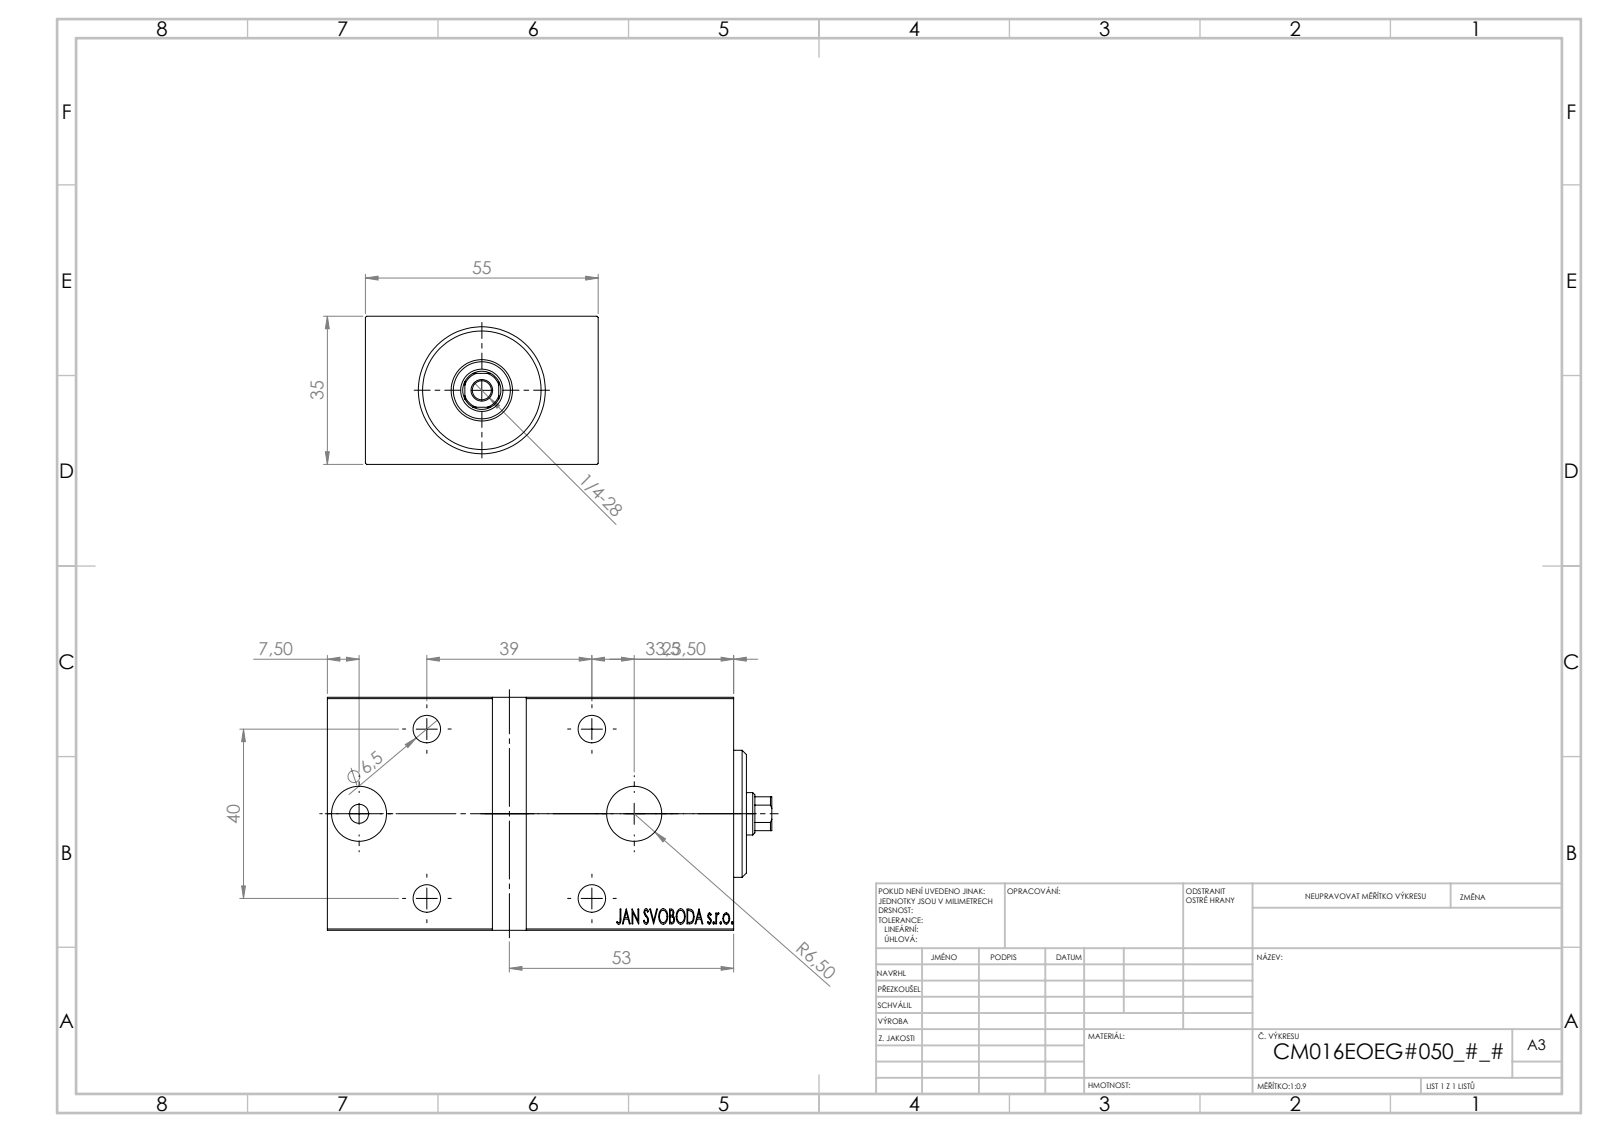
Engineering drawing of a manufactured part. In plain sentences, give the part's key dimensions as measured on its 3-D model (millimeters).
The part is named "V450CM_E_Body; V450CM_E_VCP; V450CM_VC_B". Its 3-D file was written by "SolidWorks 2019 (CONFIG_CONTROL_DESIGN)". It is 3 solids with 852 faces: 410 planar, 48 cylindrical and 394 other. Overall it measures 105 by 55 by 35 millimeters. Its volume is 174 409 cubic millimeters and its surface area 36 700 square millimeters. Round holes: 4 of diameter 6.5, 4 of diameter 10.5, 2 of diameter 13, 1 of diameter 4.5, 1 of diameter 10, 1 of diameter 13.5, 1 of diameter 14.5, 1 of diameter 16, 1 of diameter 25. Round bosses or shafts: 1 of diameter 30, 1 of diameter 18, 1 of diameter 4.5. Partial cylindrical surfaces (rounded edges, fillets, slot ends): 1 of radius 4.5. The main face-to-face distances are 35, 55, 96, 5, 91, 8, 2, 1, 3, 99. The hole center spacings are 22.36, 25.61, 39, 40, 52.92, 55.87, 58.52, 65.
